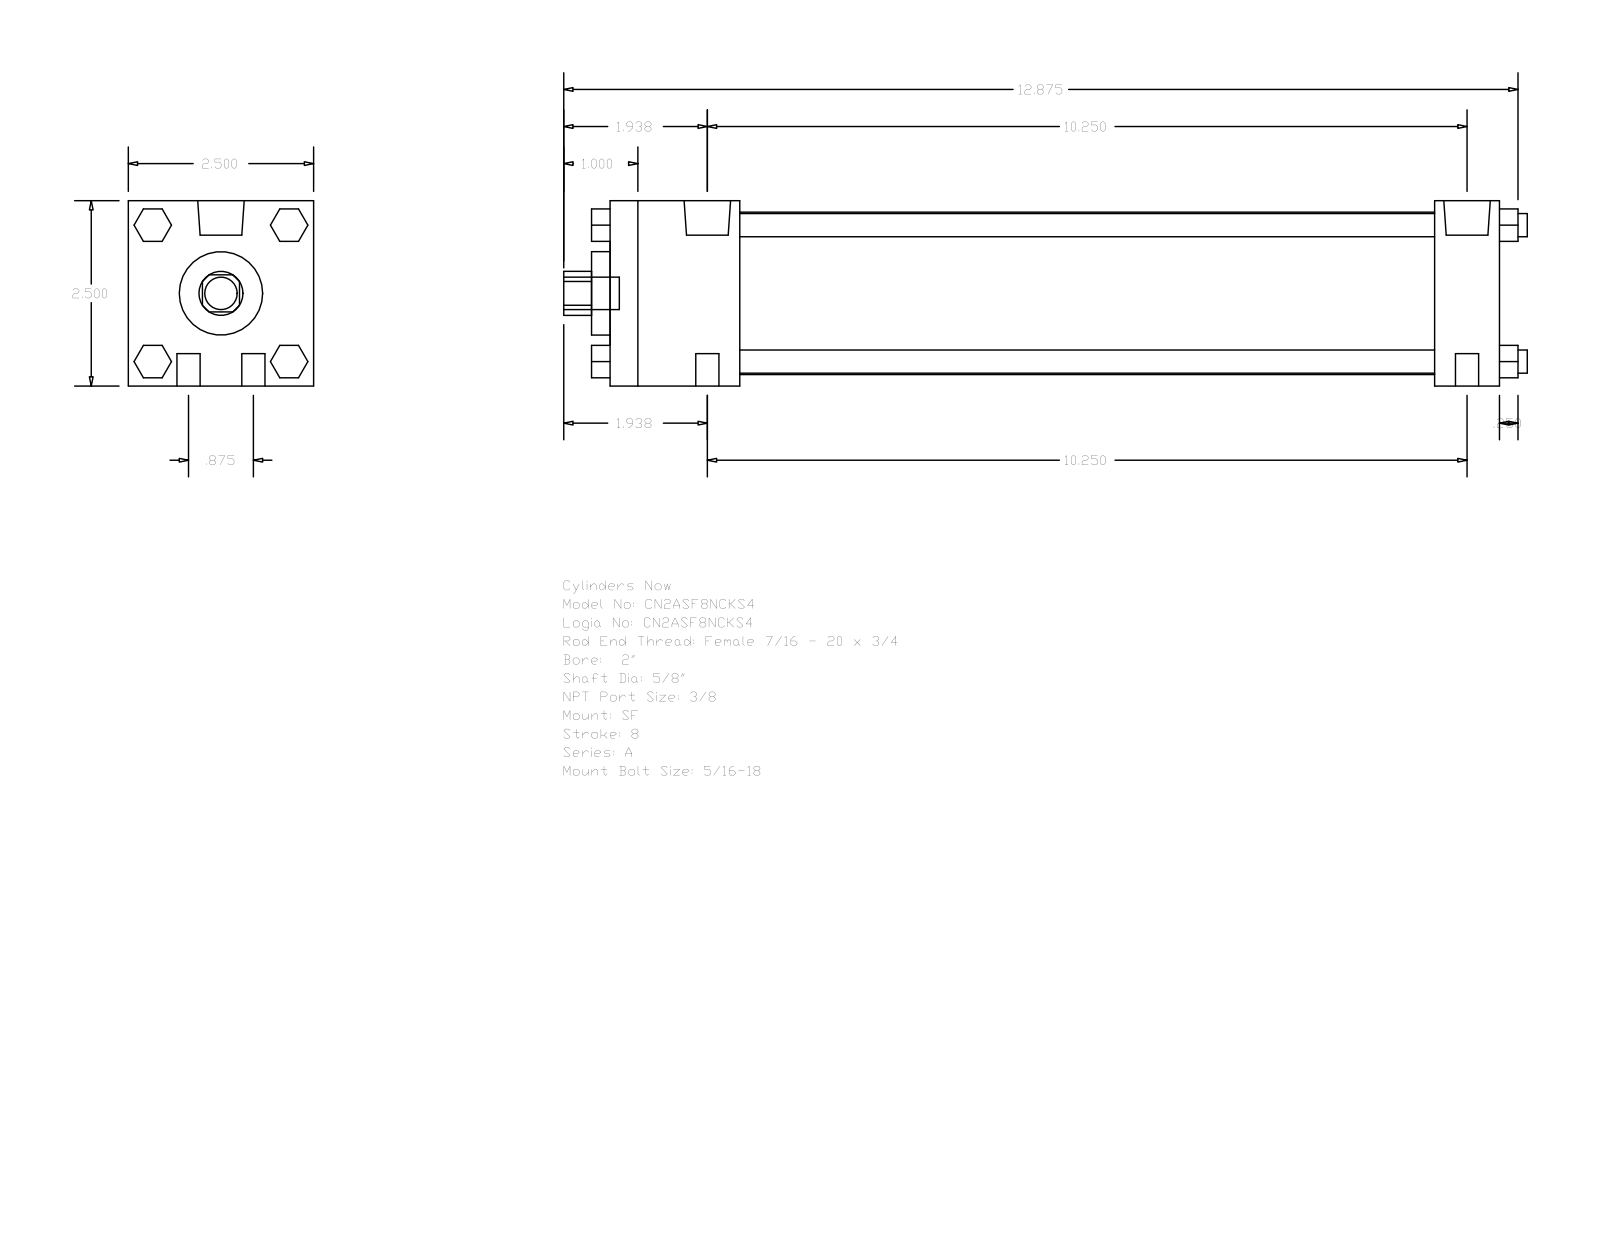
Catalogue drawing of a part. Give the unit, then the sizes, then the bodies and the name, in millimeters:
Units: millimetres
Overall size (bounding box): 330.2 × 63.5 × 63.5
Round holes (diameter × count): ⌀15.88 ×1, ⌀28.57 ×1, ⌀55.63 ×1
Round bosses / shafts (diameter × count): ⌀7.94 ×8, ⌀15.93 ×2, ⌀5.56 ×2, ⌀11.11 ×1
Partial cylindrical surfaces — rounded edges, fillets, slot ends (radius × count): R7.54 ×1
Main face-to-face distances: 63.5, 304.8, 282.57, 22.23, 44.45, 238.12, 260.35, 50.8, 311.15, 6.35
Bodies: 0 solids, 124 faces (94 planar, 30 cylindrical, 0 other)
Part name (STEP PRODUCT): A_SF__0200_0.625
STEP written by: GSSL Pune (CONFIG_CONTROL_DESIGN)
